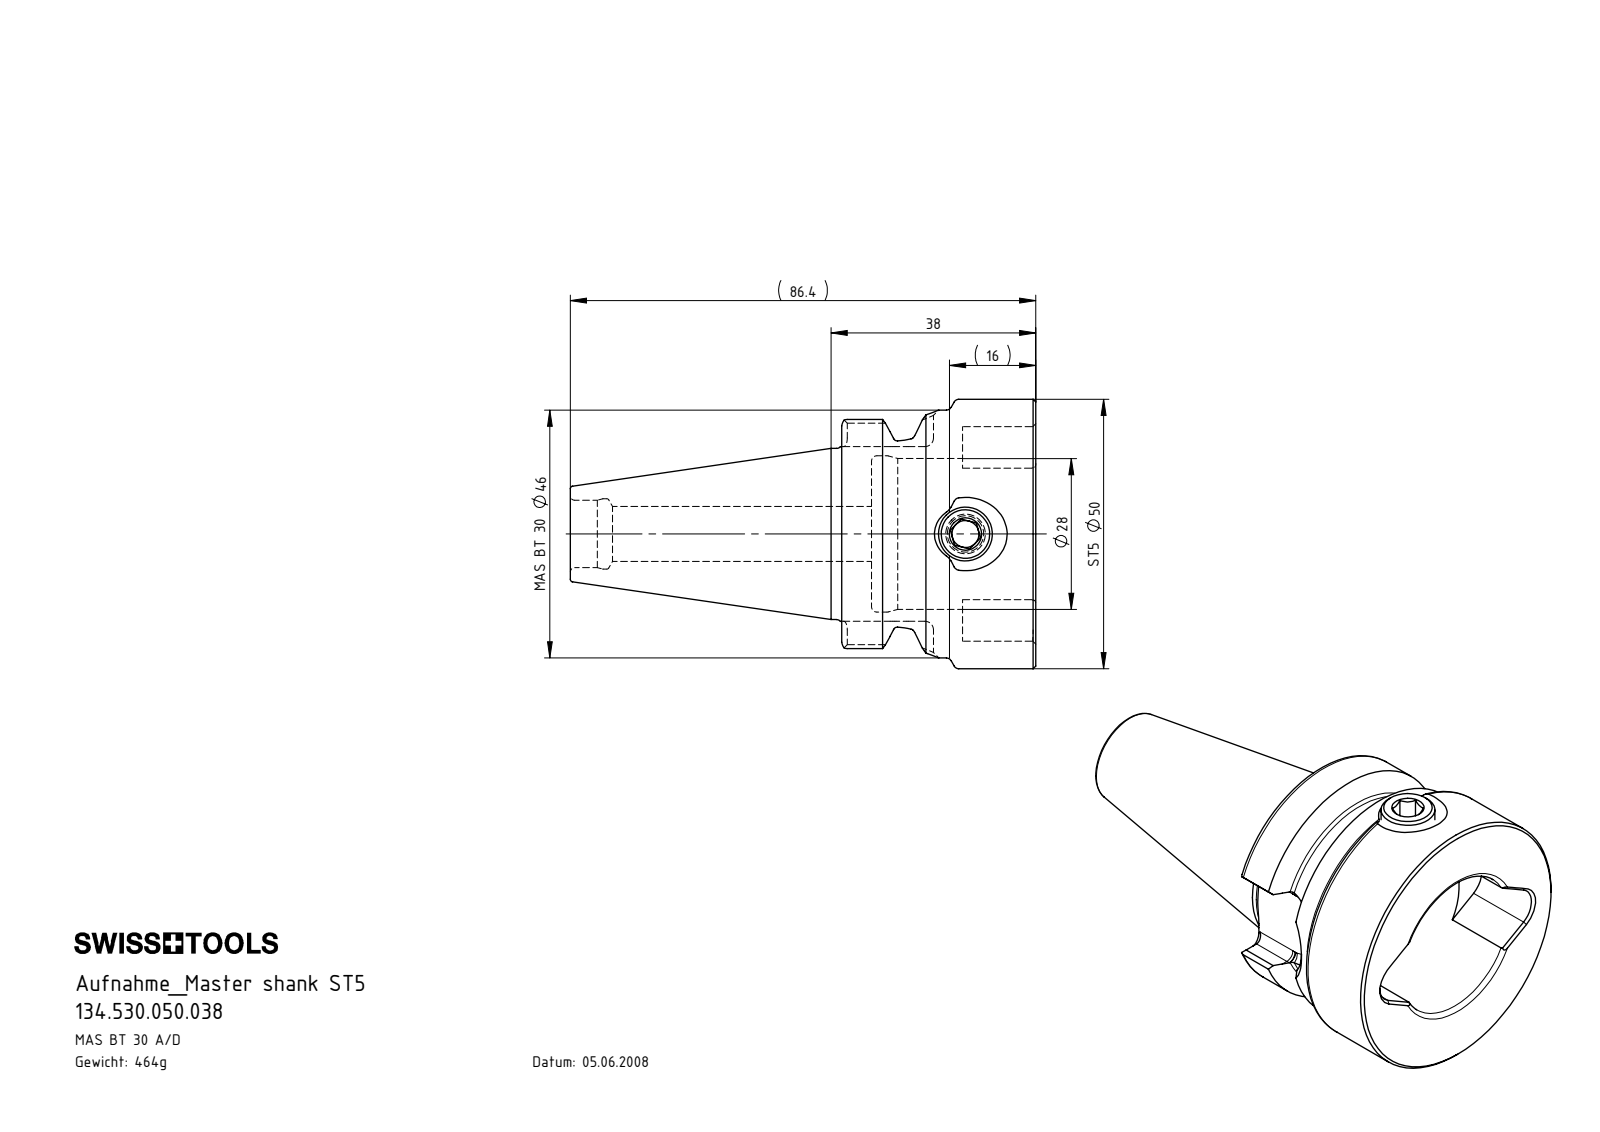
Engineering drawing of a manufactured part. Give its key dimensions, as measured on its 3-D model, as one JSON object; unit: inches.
{"part_name": "ST5-ER1.001.012_A; BT3-ST5.K01.038; BT3-ST5.K01.038_A", "step_written_by": "SolidWorks 2015 (CONFIG_CONTROL_DESIGN)", "units": "inches", "bodies": {"solids": 2, "faces": 153, "planar": 35, "cylindrical": 42, "other": 76}, "overall_size": [3.402, 1.969, 1.969], "volume_in3": 3.615, "surface_area_in2": 28.17, "round_holes": [[0.354, 1], [0.402, 1], [0.492, 1], [0.514, 1], [1.102, 1], [1.142, 1]], "round_bosses_or_shafts": [[1.969, 1], [1.811, 1], [1.25, 1], [0.394, 1]], "partial_cylinders_radius": [[0.063, 8], [0.165, 2], [0.317, 1], [0.748, 1]], "face_to_face_distances": [1.201, 0.217, 1.417, 1.276, 0.949, 0.882, 0.665, 0.535, 1.984, 2.201]}
